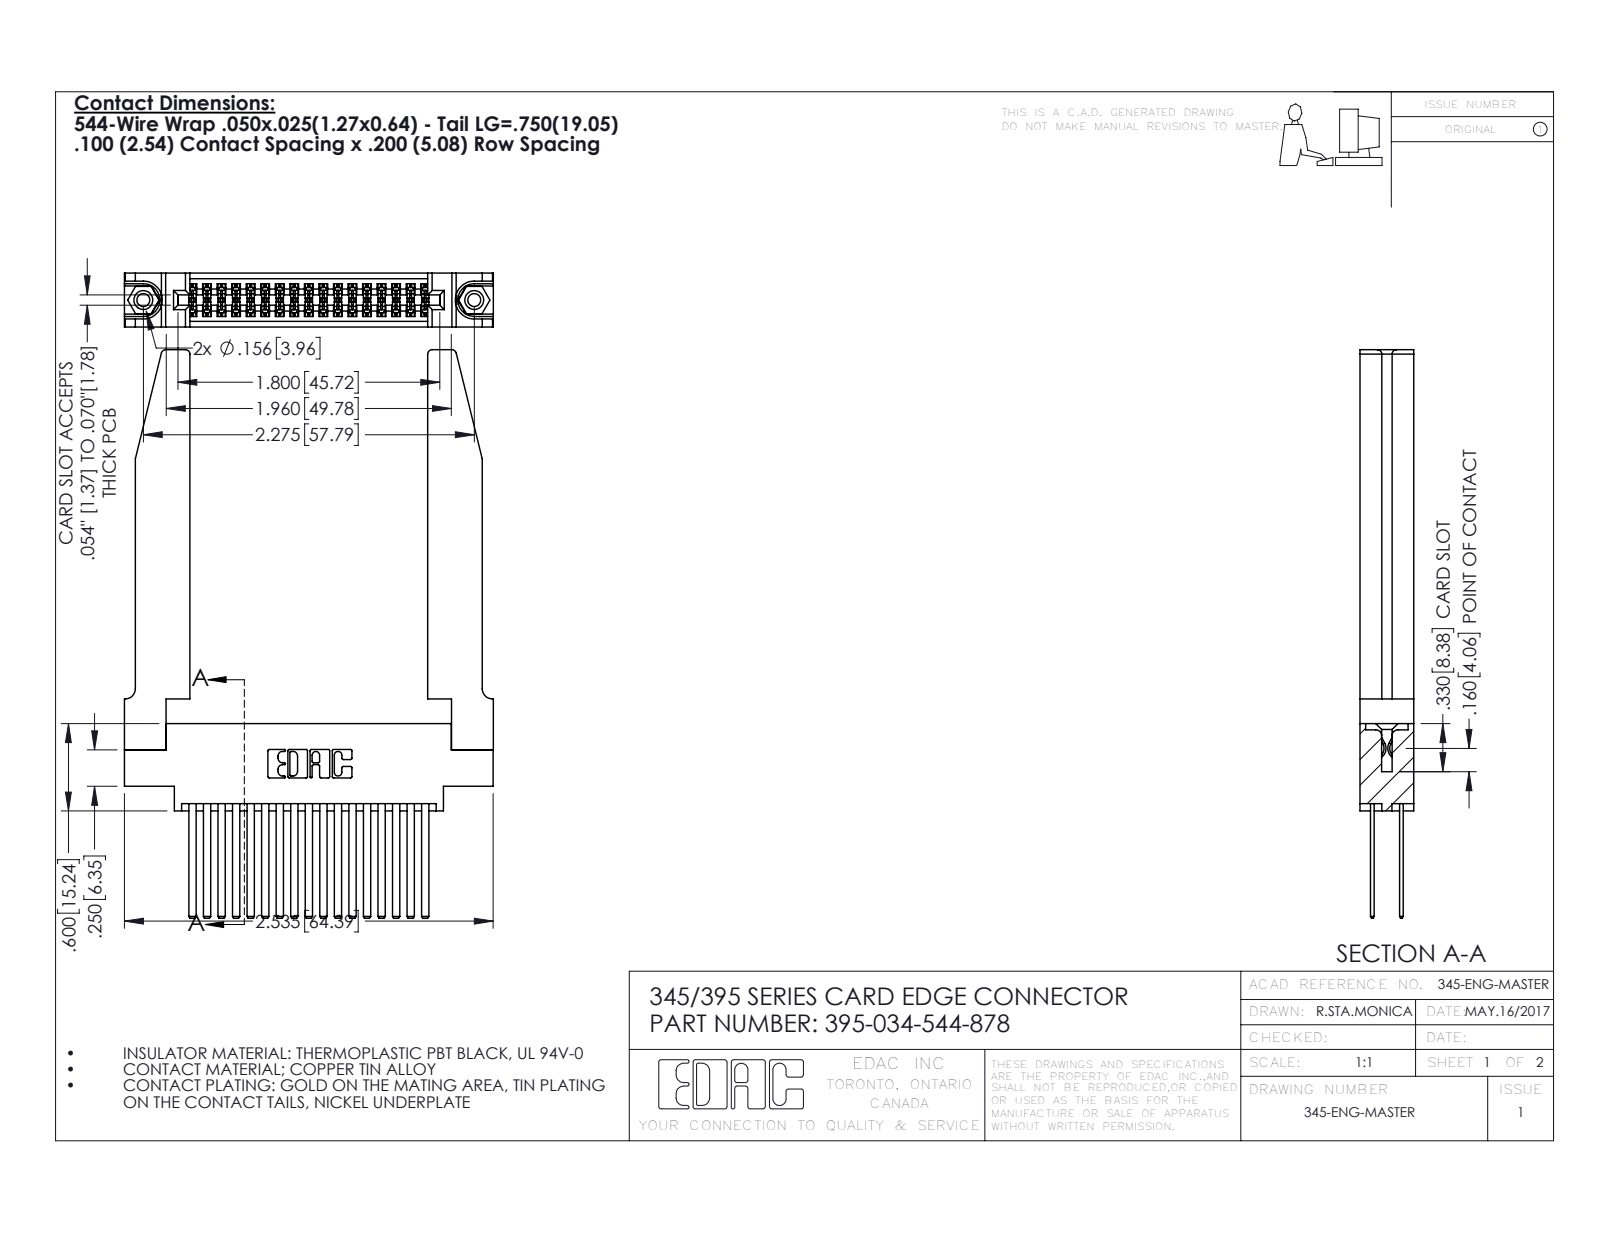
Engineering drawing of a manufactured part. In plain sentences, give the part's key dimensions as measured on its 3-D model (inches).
The part is named "345 Part_0.170 Offset - 0.156 Dia-TH; 345-292-001_345-293-144; 395-034-544-878; 345-250-001_345-250-001-102 (+1 more)". Its 3-D file was written by "SolidWorks 2016 (CONFIG_CONTROL_DESIGN)". It is 39 solids with 1860 faces: 1212 planar, 596 cylindrical and 52 other. Overall it measures 3.907 by 2.536 by 0.37 inches. Its volume is 0.864 cubic inches and its surface area 26.87 square inches. Round holes: 2 of diameter 0.089, 2 of diameter 0.125, 2 of diameter 0.156, 1 of diameter 0.064. Round bosses or shafts: 2 of diameter 0.155. Partial cylindrical surfaces (rounded edges, fillets, slot ends): 51 of radius 0.006, 22 of radius 0.01, 8 of radius 0.03, 6 of radius 0.007, 6 of radius 0.031, 3 of radius 0.026, 2 of radius 0.014, 2 of radius 0.019. The main face-to-face distances are 0.37, 0.072, 0.298, 0.098, 0.272, 0.025, 0.2, 0.225, 0.175, 0.148. The hole center spacings are 0.27, 2.041, 2.275.
